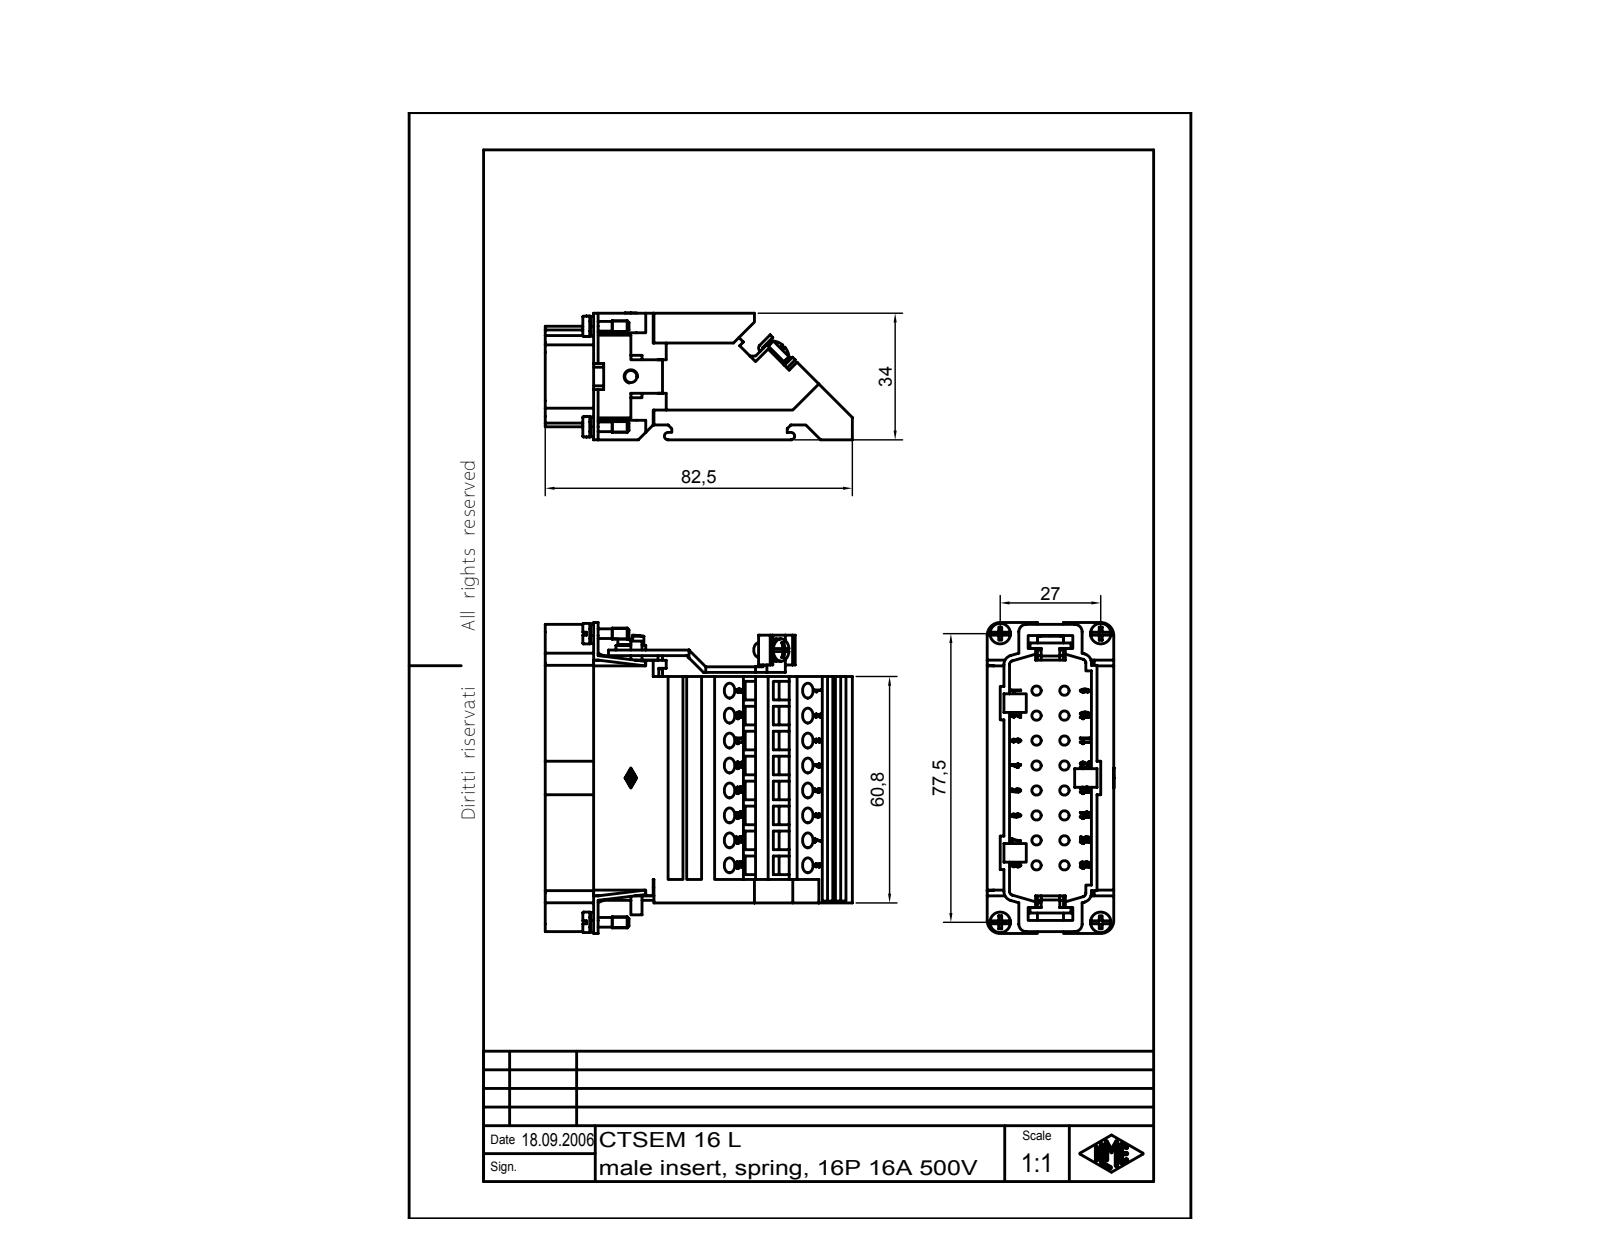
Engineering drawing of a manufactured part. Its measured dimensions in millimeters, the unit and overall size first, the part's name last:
Units: millimetres
Overall size (bounding box): 83.5 × 82.5 × 34.1
Round holes (diameter × count): ⌀4 ×16, ⌀3.24 ×1
Round bosses / shafts (diameter × count): ⌀2.5 ×16, ⌀5.5 ×2, ⌀5.3 ×2, ⌀3 ×2, ⌀2.6 ×2, ⌀8 ×1, ⌀7 ×1, ⌀6 ×1
Partial cylindrical surfaces — rounded edges, fillets, slot ends (radius × count): R0.1 ×14, R1 ×10, R2 ×6, R2.5 ×4, R0.2 ×2, R3.5 ×2
Main face-to-face distances: 4, 1.5, 4.5, 2, 6, 28, 34, 23.5, 2.5, 29.5
Hole centre spacings: 6.7, 24.31, 13.4, 26.94, 20.1, 30.82, 23.37, 26.8
Volume: 112 048 mm³ · Surface area: 34 719 mm²
Bodies: 1 solid, 1410 faces (802 planar, 134 cylindrical, 474 other)
Part name (STEP PRODUCT): CTSEM 16 L
STEP written by: Autodesk Inventor 7 (AUTOMOTIVE_DESIGN)
